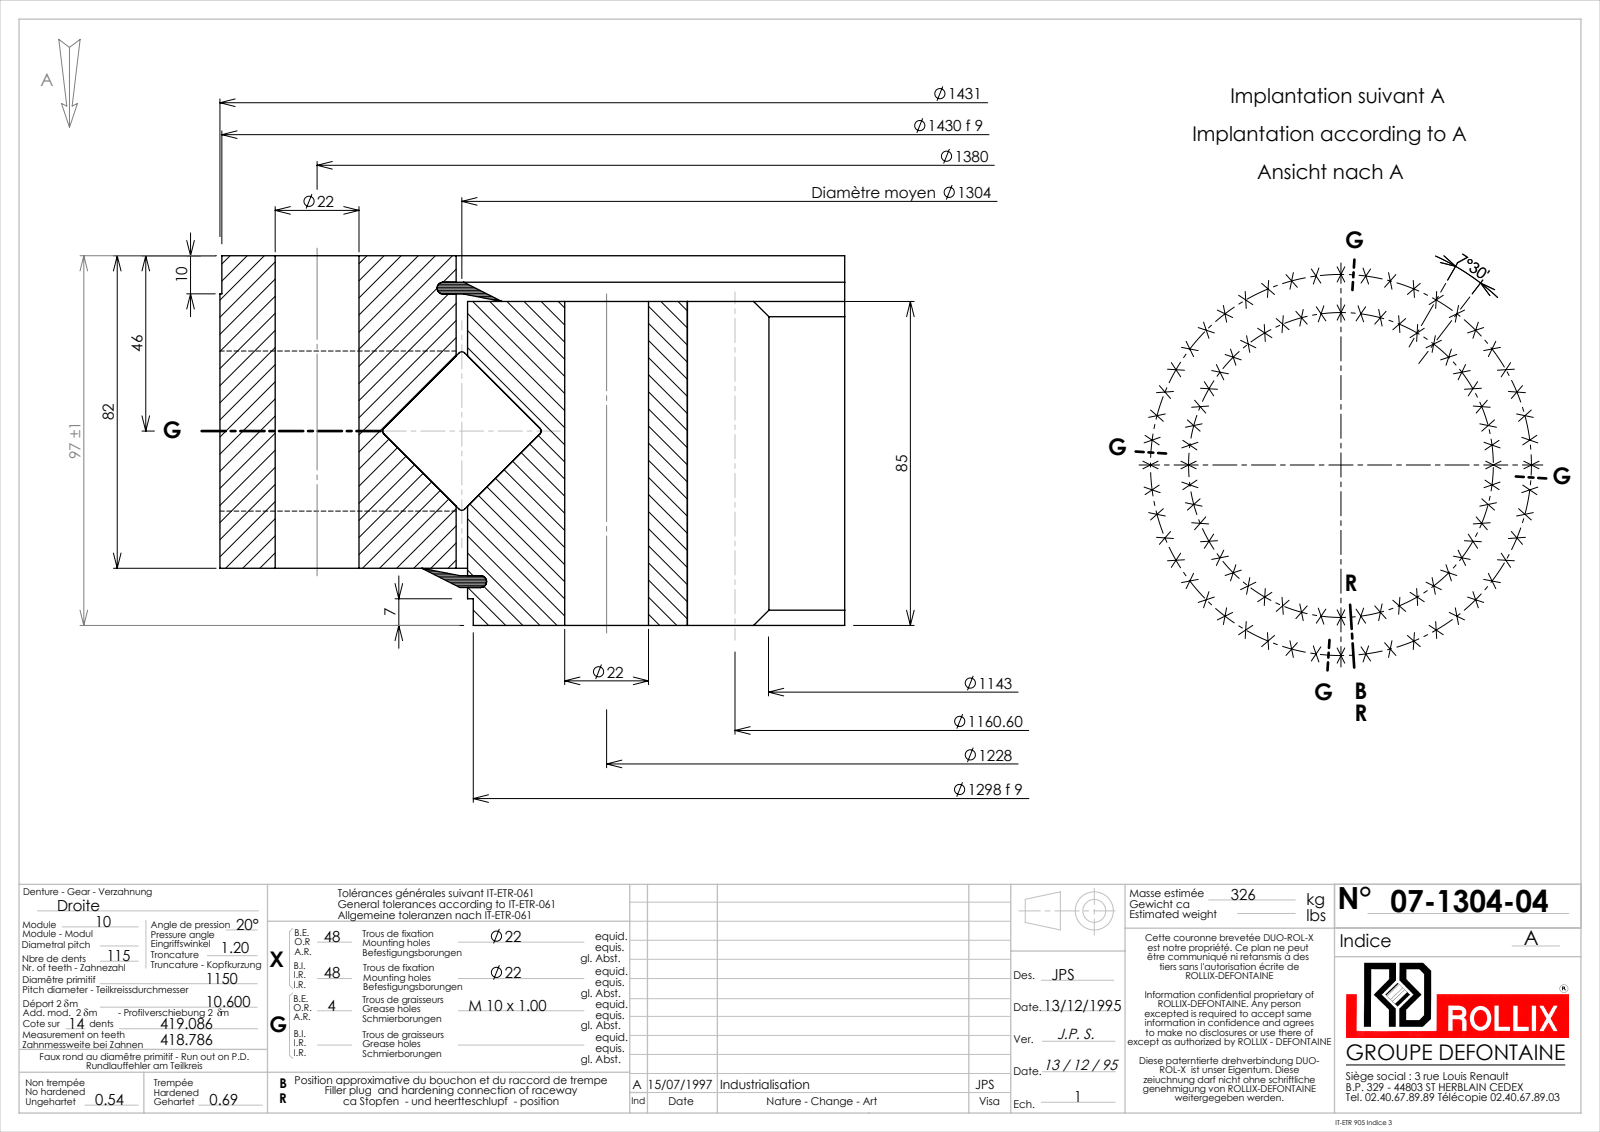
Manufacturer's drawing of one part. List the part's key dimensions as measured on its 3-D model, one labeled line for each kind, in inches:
Part name (STEP PRODUCT): 07-1304-04
STEP written by: SolidWorks 2016 (CONFIG_CONTROL_DESIGN)
Units: inches
Bodies: 5 solids, 969 faces (246 planar, 451 cylindrical, 272 other)
Overall size (bounding box): 56.339 × 56.339 × 3.819
Volume: 2 349 in³ · Surface area: 5 746 in²
Round holes (diameter × count): ⌀0.866 ×96, ⌀0.354 ×4, ⌀51.457 ×1
Round bosses / shafts (diameter × count): ⌀56.339 ×1, ⌀56.299 ×1, ⌀51.22 ×1, ⌀51.102 ×1, ⌀1.181 ×1
Partial cylindrical surfaces — rounded edges, fillets, slot ends (radius × count): R22.5 ×1, R23.339 ×1
Main face-to-face distances: 3.228, 2.756, 0.472, 0.591, 3.346, 3.819, 0.077, 2.833, 0.199, 2.955
Hole centre spacings: 12.513, 21.383, 15.541, 9.432, 26.86, 6.311, 36.349, 3.162
